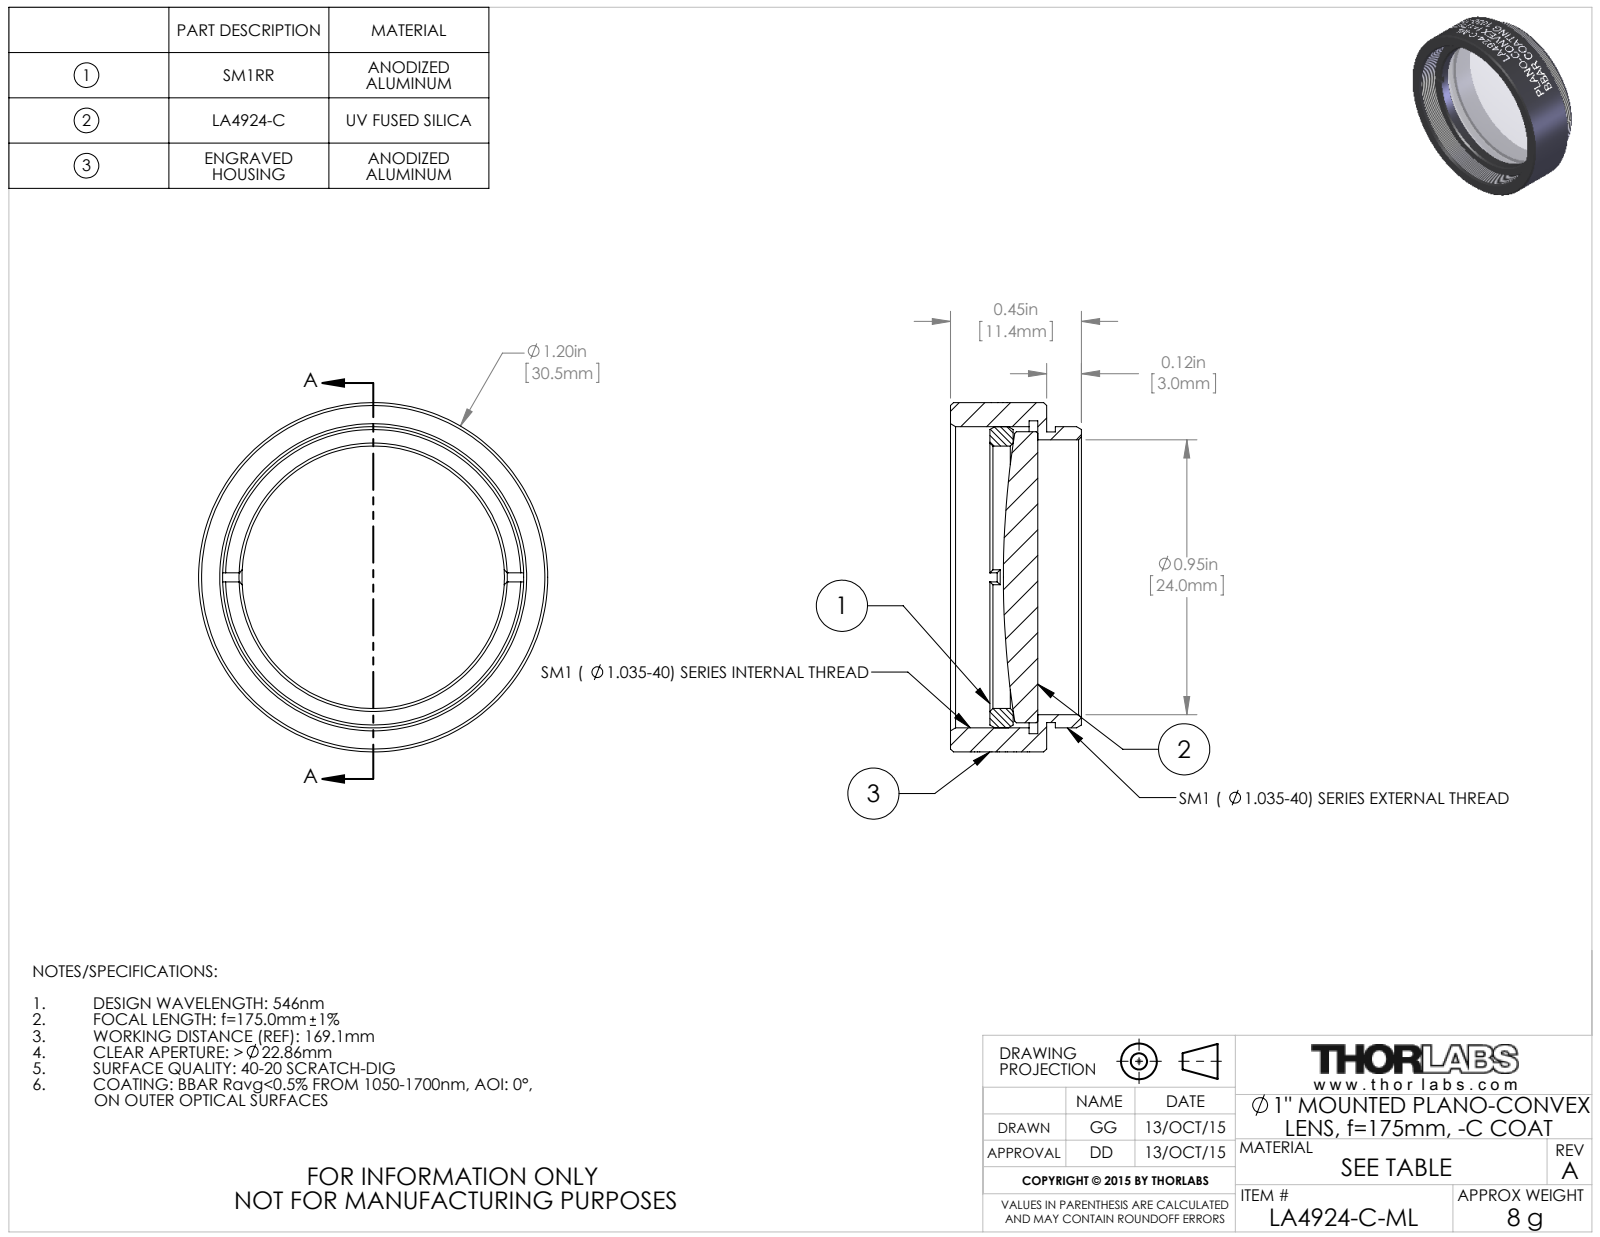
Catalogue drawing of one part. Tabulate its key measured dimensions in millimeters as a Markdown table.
| quantity | value |
| --- | --- |
| part name | TTN039446-E0W |
| STEP written by | SolidWorks 2014 (CONFIG_CONTROL_DESIGN) |
| units | millimeters |
| bodies | 3 solids, 162 faces (20 planar, 114 cylindrical, 28 other) |
| overall size | 30.48 × 30.48 × 11.43 |
| volume | 3 350 mm³ |
| surface area | 4 304 mm² |
| round holes (diameter × count) | 22.91 × 1, 24 × 1, 27.31 × 1 |
| round bosses / shafts (diameter × count) | 30.48 × 1, 26.29 × 1, 25.4 × 1, 25.37 × 1 |
| main face-to-face distances | 0.76, 8.38, 7.62, 2.92, 2.16, 5.46, 4.95, 4.19, 2.03, 3.43 |
